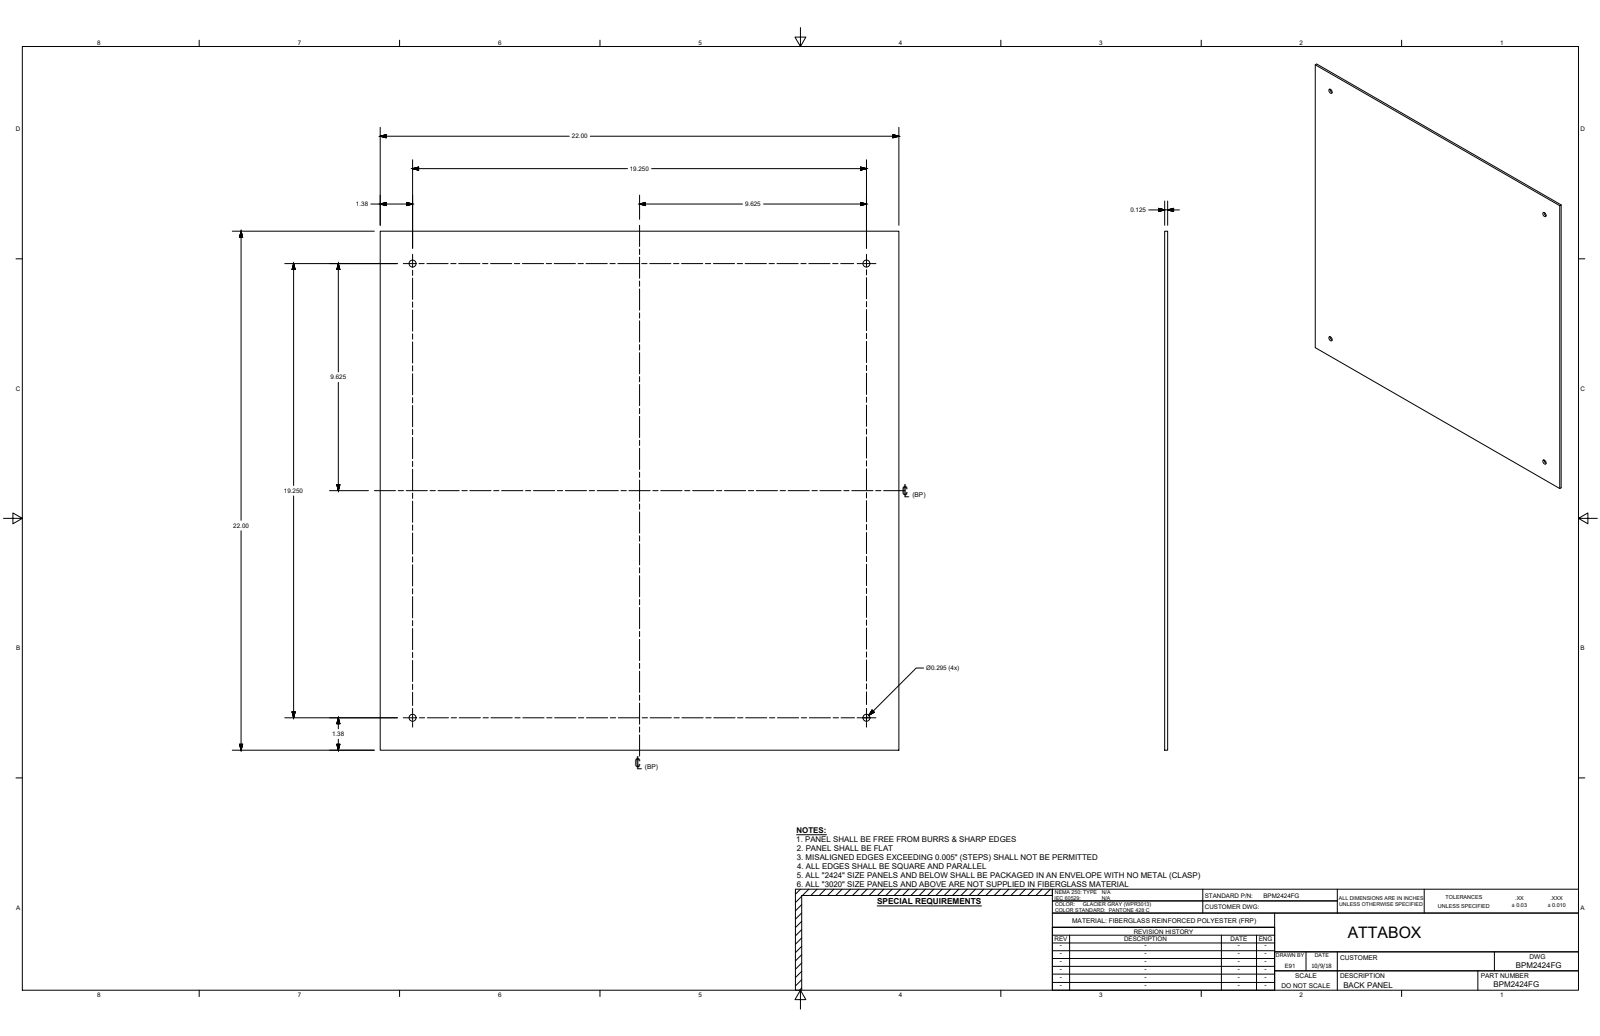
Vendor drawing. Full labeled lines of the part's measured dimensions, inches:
Part name (STEP PRODUCT): HW-MP2424FG
STEP written by: Autodesk Inventor 2017 (CONFIG_CONTROL_DESIGN)
Units: inches
Bodies: 1 solid, 10 faces (6 planar, 4 cylindrical, 0 other)
Overall size (bounding box): 22 × 22 × 0.125
Volume: 60.47 in³ · Surface area: 978.9 in²
Round holes (diameter × count): ⌀0.295 ×4
Main face-to-face distances: 0.125, 22
Hole centre spacings: 19.25, 27.224
